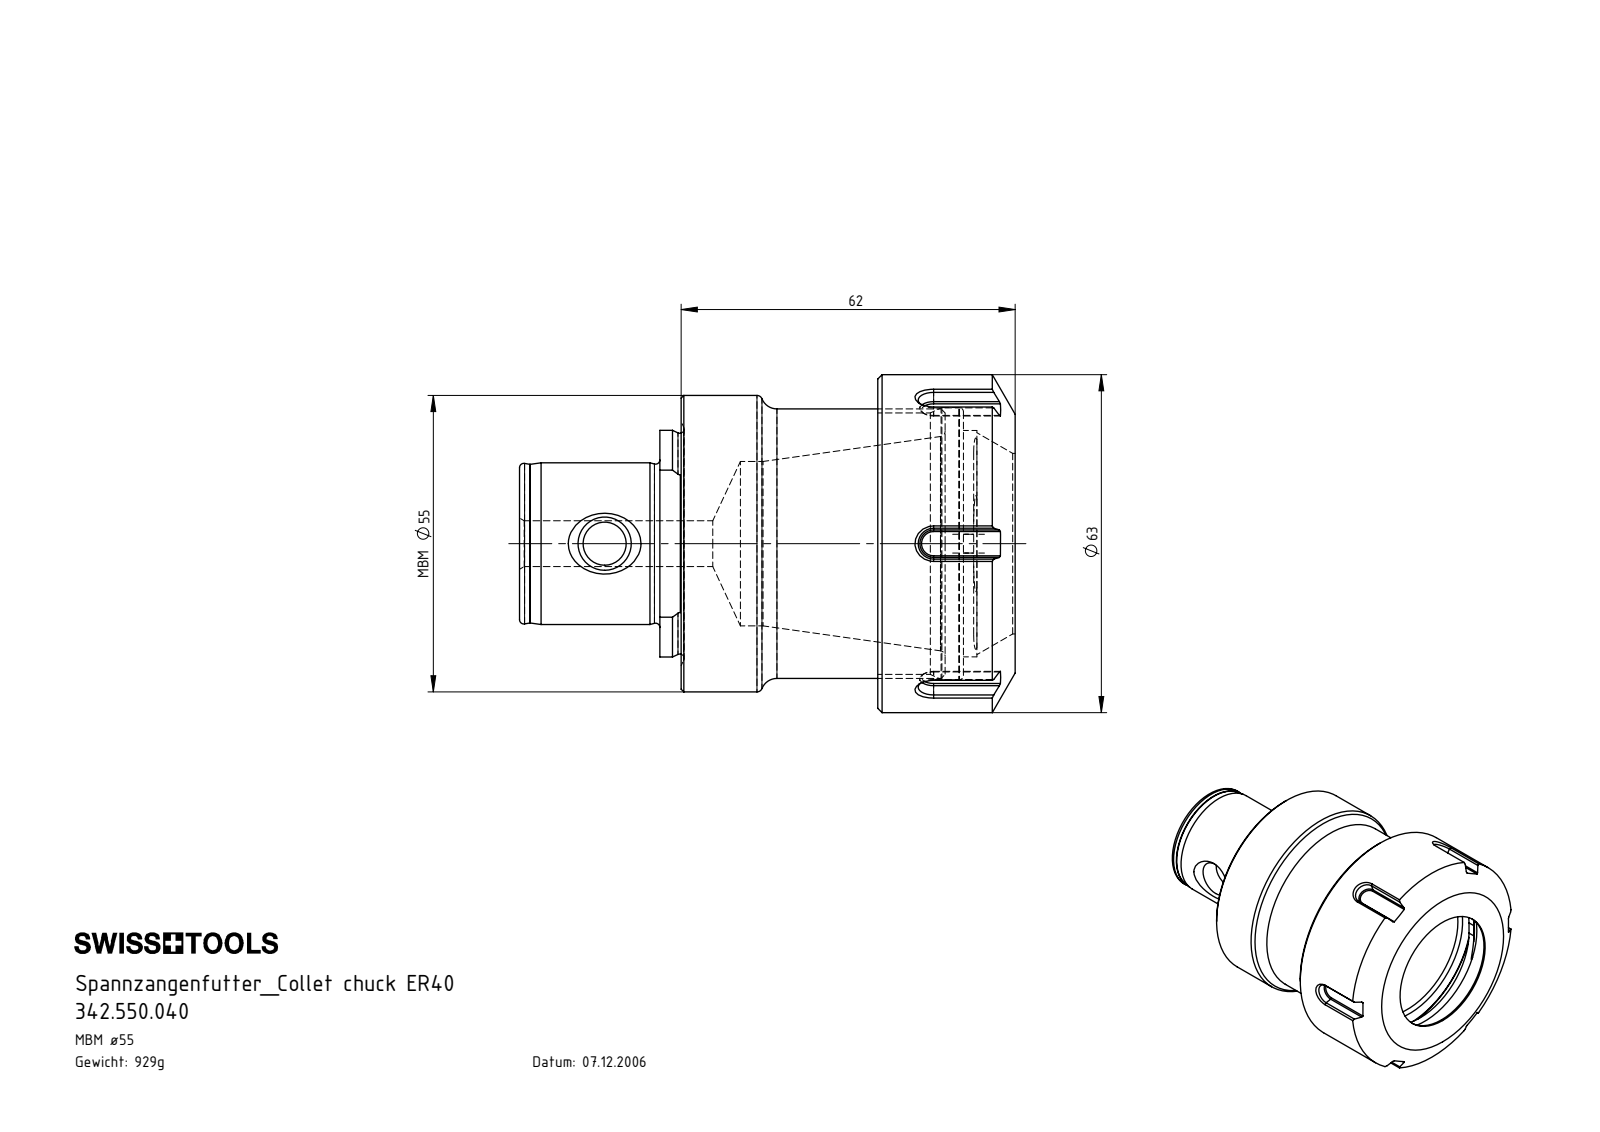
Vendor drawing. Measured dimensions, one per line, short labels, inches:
name: E40-ER1.001.025; MB5-E40.K01.062_D; MB5.E40.K01.062
written by: SolidWorks 2017 (AUTOMOTIVE_DESIGN)
unit: in
bodies: 2 solids, 118 faces (59 planar, 14 cylindrical, 45 other)
size: 3.622 × 2.469 × 2.469
volume: 7.219 in³; area: 50.4 in²
holes: 1× ⌀0.315, 1× ⌀0.335, 1× ⌀1.201, 1× ⌀1.319, 1× ⌀1.909, 1× ⌀1.988
bosses: 1× ⌀2.469, 1× ⌀2.165, 1× ⌀1.969, 1× ⌀1.181
rounds: 2× R0.758, 1× R0.828
face distances: 1.004, 1.437, 2.441, 2.063, 0.626, 0.378, 1.181, 2.618, 3.244, 3.622
